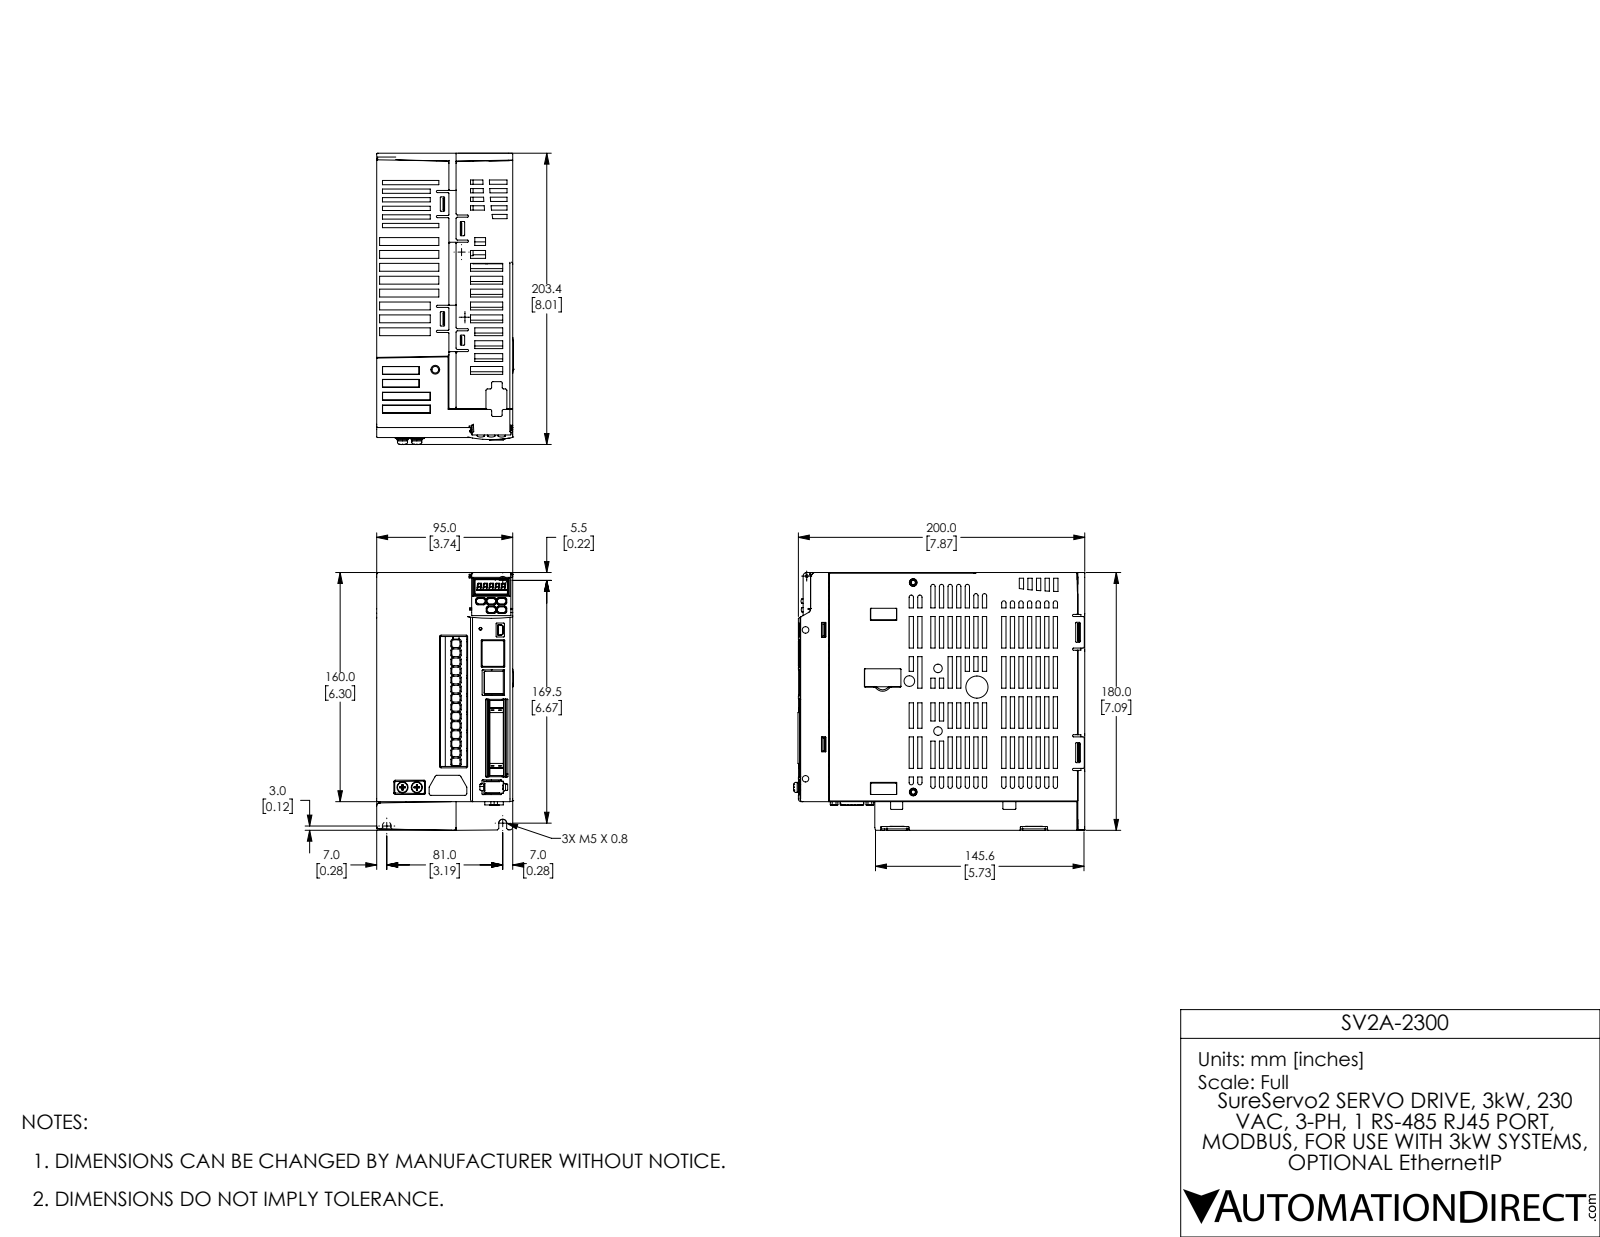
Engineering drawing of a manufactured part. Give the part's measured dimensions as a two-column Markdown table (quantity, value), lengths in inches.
| quantity | value |
| --- | --- |
| part name | 0-sv2a-2200-2300 Red2 fXT comb1E minus comb wcomb Bc5 r1 |
| STEP written by | SolidWorks 2017 (AUTOMOTIVE_DESIGN) |
| units | inches |
| bodies | 3 solids, 5390 faces (3184 planar, 1408 cylindrical, 798 other) |
| overall size | 8.008 × 7.089 × 3.76 |
| volume | 189.6 in³ |
| surface area | 462.3 in² |
| round holes (diameter × count) | 0.02 × 5, 0.177 × 3, 0.067 × 2, 0.118 × 2, 0.157 × 2, 0.213 × 2, 0.236 × 2, 0.059 × 1, 0.169 × 1, 0.183 × 1, 0.217 × 1, 0.295 × 1 |
| round bosses / shafts (diameter × count) | 0.307 × 2, 0.276 × 2, 0.256 × 2, 0.197 × 2, 1.339 × 1 |
| partial cylindrical surfaces (radius × count) | 0.02 × 355, 0.059 × 148, 0.012 × 139, 0.039 × 120, 0.008 × 101, 0.016 × 22, 0.03 × 21, 0.028 × 14 |
| main face-to-face distances | 0.098, 3.74, 0.024, 3.716, 3.642, 0.074, 0.029, 6.27, 6.299, 0.039 |
| hole center spacings | 0.165, 0.331, 0.496, 0.275, 0.278, 0.359, 0.394, 0.487 |
